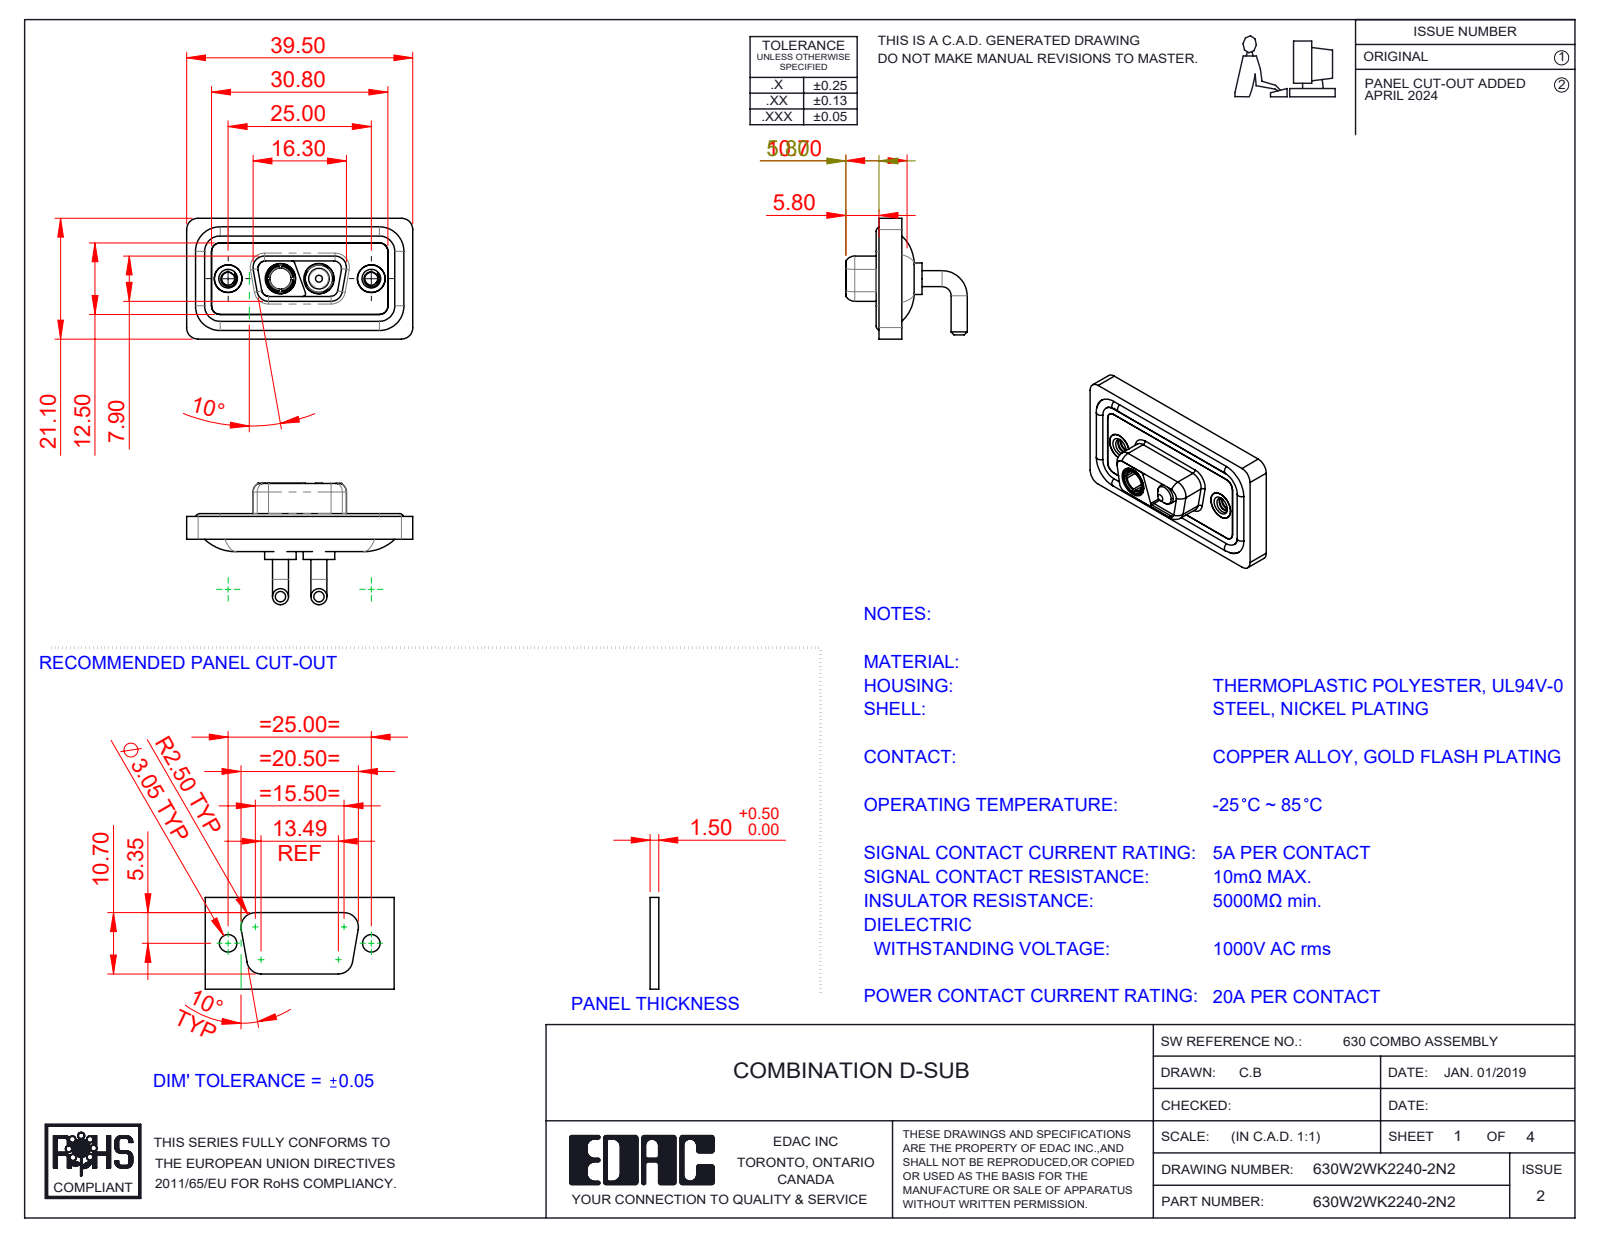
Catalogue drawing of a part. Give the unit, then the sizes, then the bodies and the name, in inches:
Units: inches
Overall size (bounding box): 1.555 × 0.835 × 0.831
Round holes (diameter × count): ⌀0.191 ×4, ⌀0.089 ×2, ⌀0.157 ×2, ⌀0.159 ×2, ⌀0.197 ×2, ⌀0.209 ×2, ⌀0.146 ×1
Round bosses / shafts (diameter × count): ⌀0.11 ×4, ⌀0.063 ×4, ⌀0.217 ×2, ⌀0.205 ×2, ⌀0.195 ×2, ⌀0.189 ×2, ⌀0.187 ×2, ⌀0.148 ×2
Partial cylindrical surfaces — rounded edges, fillets, slot ends (radius × count): R0.059 ×18, R0.079 ×18, R0.053 ×8, R0.063 ×8, R0.02 ×6, R0.01 ×4, R0.024 ×4, R0.026 ×4
Main face-to-face distances: 0.016, 0.043, 0.114, 0.071, 0.098, 0.063, 0.122, 0.059, 0.083, 0.146
Hole centre spacings: 0.36, 0.624, 0.265, 0.984
Volume: 0.287 in³ · Surface area: 11.62 in²
Bodies: 11 solids, 508 faces (144 planar, 235 cylindrical, 129 other)
Part name (STEP PRODUCT): 630Combo Shell Front_09 Contacts; 630W2WK2140-2N2; 630Combo Housing_2WK2; 630Combo Waterproof Housing_09 Contacts (+4 more)
STEP written by: SolidWorks 2023 (CONFIG_CONTROL_DESIGN)
